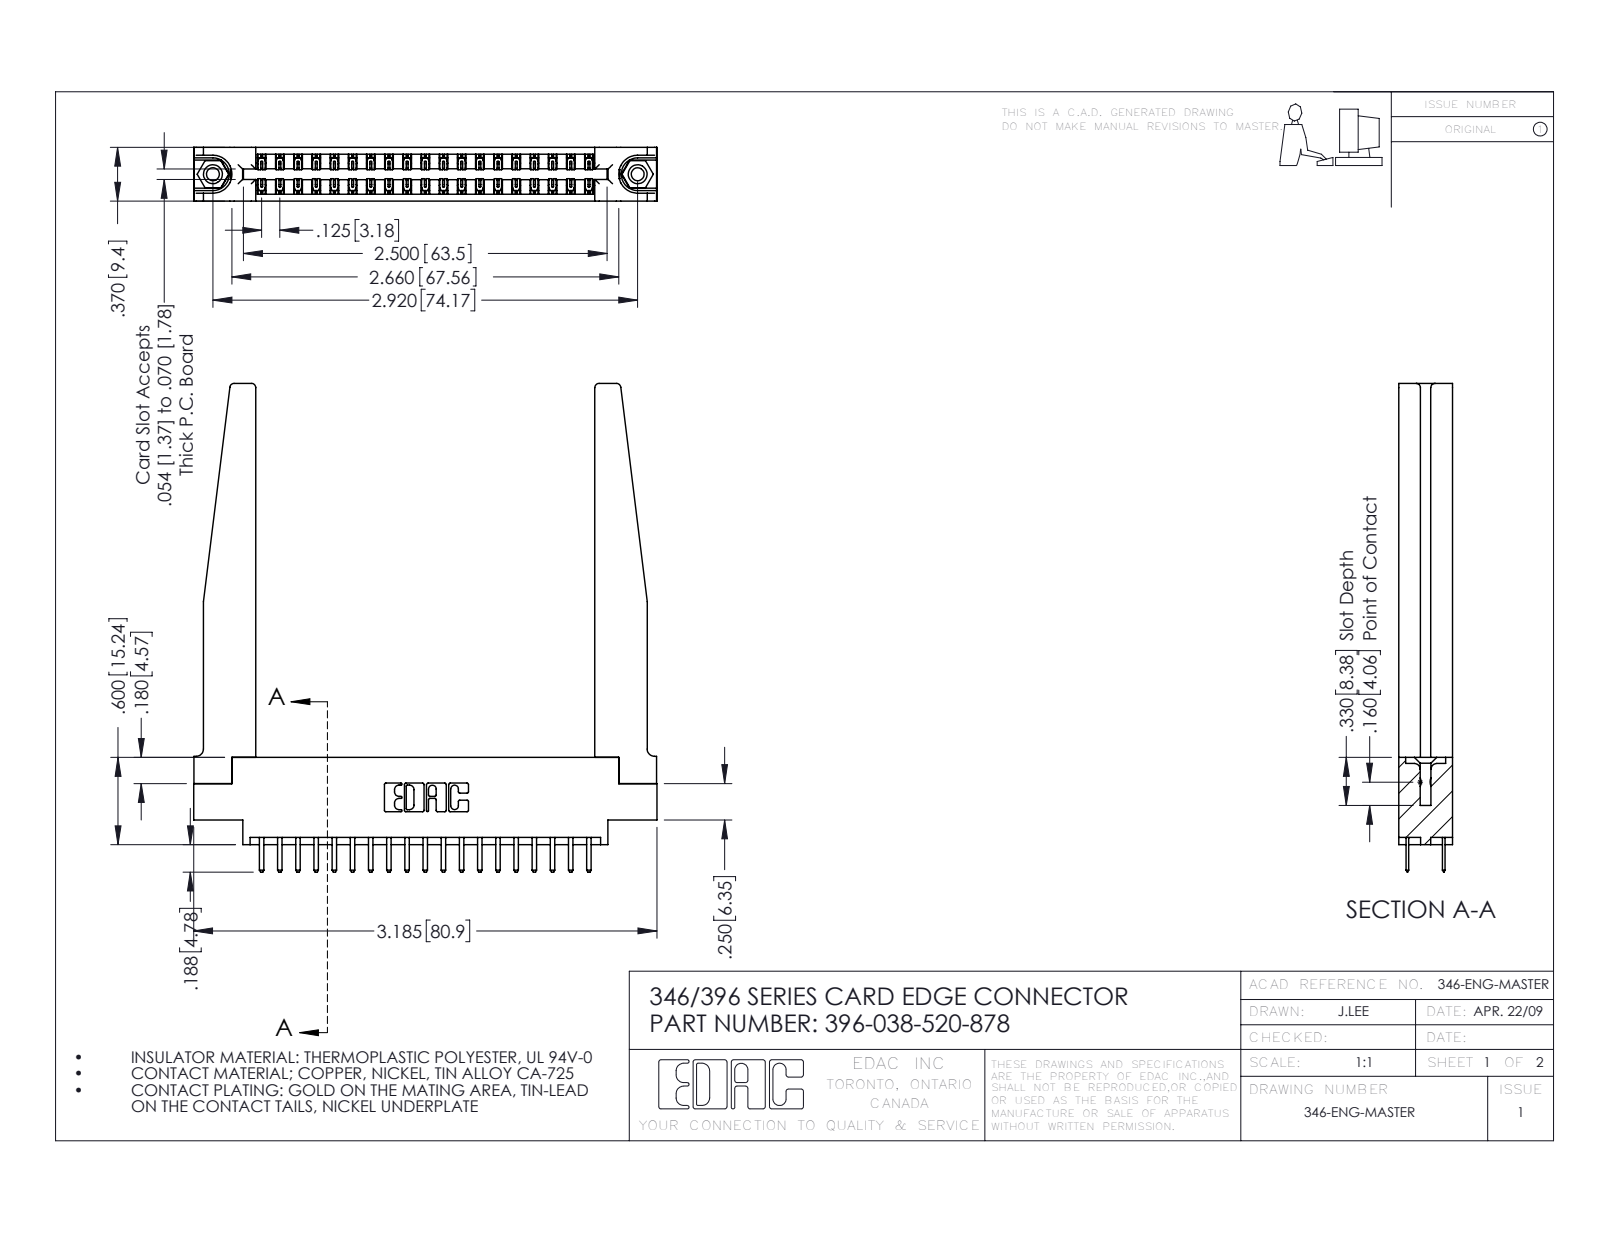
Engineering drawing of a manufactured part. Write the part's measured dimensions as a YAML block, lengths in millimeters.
part_name: "345-250-001_345-250-001-102; 396-038-520-878; 345-292-001_345-293-120; 346 Part_0.170 Offset - 0.156 Dia-TH (+1 more)"
step_written_by: "SolidWorks 2016 (CONFIG_CONTROL_DESIGN)"
units: millimeters
bodies: {solids: 43, faces: 2488, planar: 1628, cylindrical: 808, other: 52}
overall_size: [85.3, 80.9, 9.4]
volume: 14500
surface_area: 16680
round_holes:
  - {diameter: 2.3, count: 2}
  - {diameter: 3.2, count: 2}
  - {diameter: 4, count: 2}
  - {diameter: 1.6, count: 1}
round_bosses_or_shafts:
  - {diameter: 3.9, count: 2}
partial_cylinders:
  - {radius: 0.2, count: 57}
  - {radius: 0.3, count: 42}
  - {radius: 0.3, count: 22}
  - {radius: 0.8, count: 8}
  - {radius: 0.2, count: 6}
  - {radius: 0.8, count: 6}
  - {radius: 0.7, count: 3}
  - {radius: 0.4, count: 2}
face_to_face_distances: [9.4, 1.2, 8.2, 1.8, 3.8, 3.8, 6.4, 7.6, 0.6, 2.6]
hole_center_spacings: [6.2, 68.9, 74.2]
